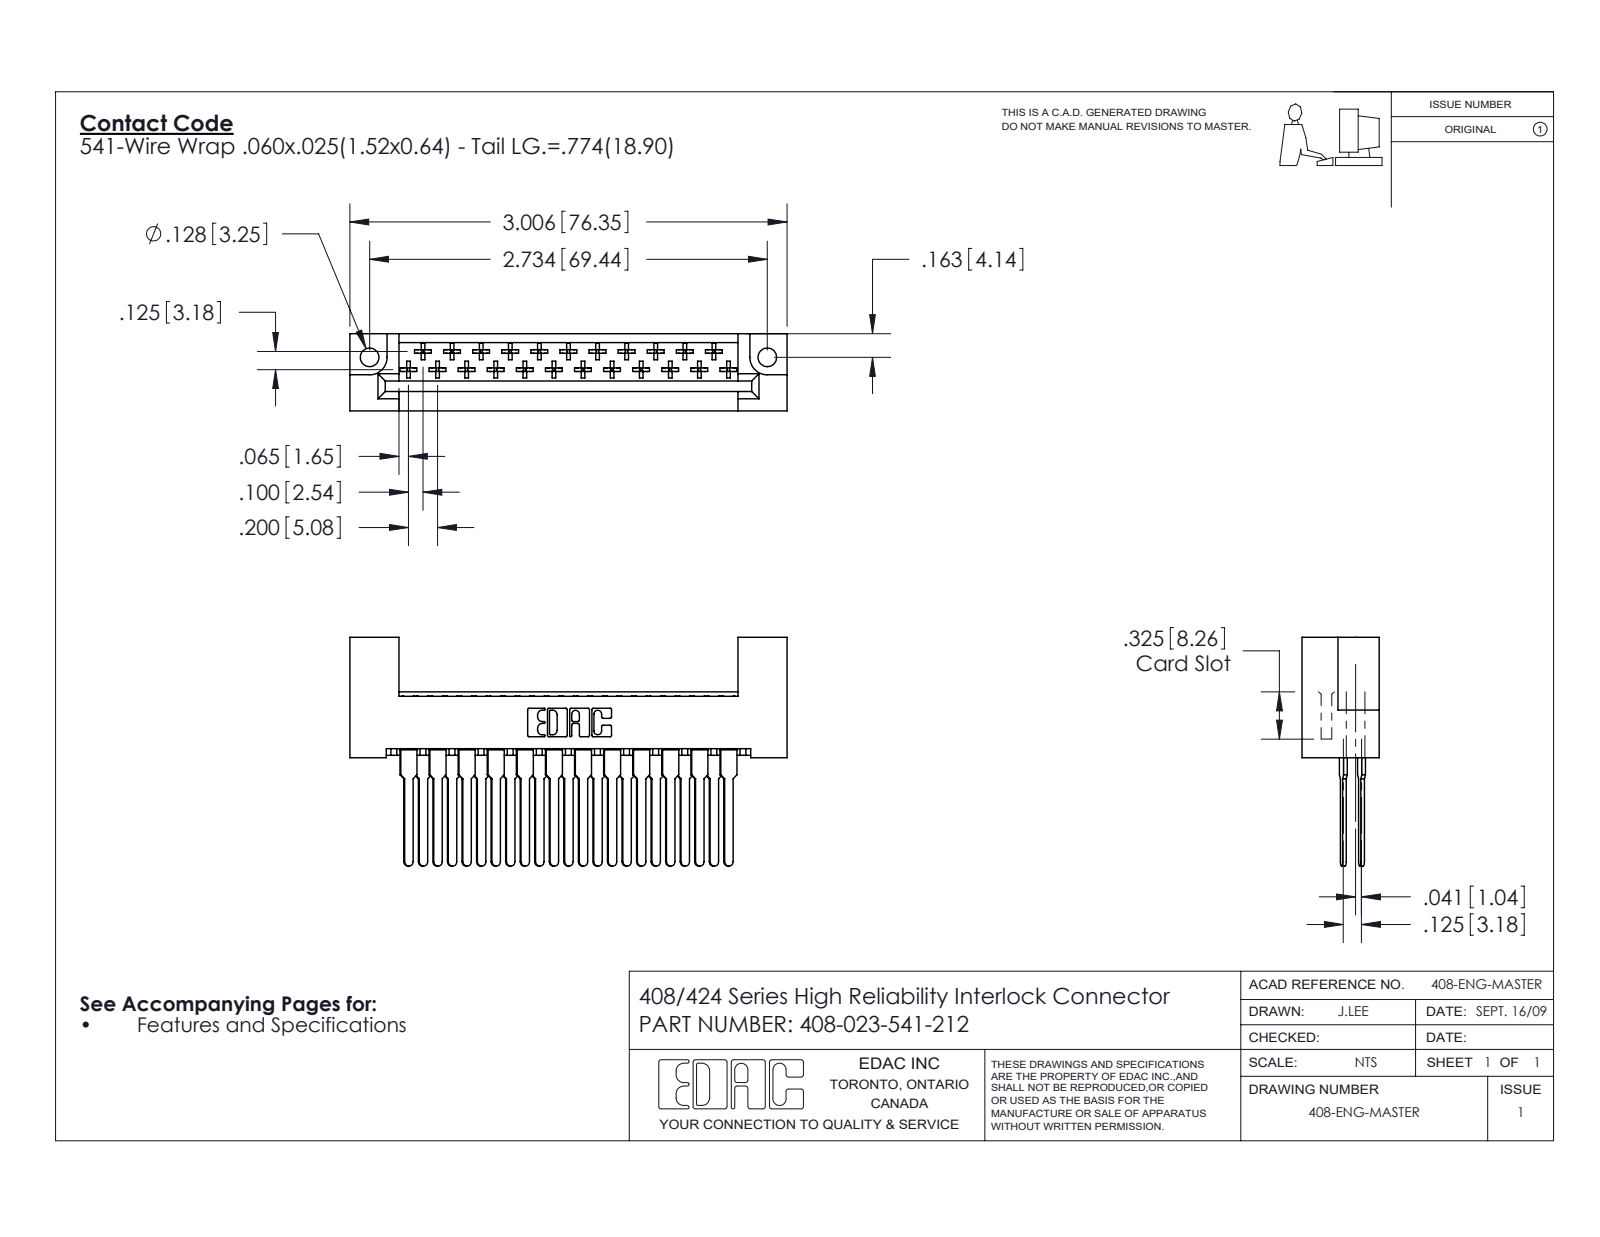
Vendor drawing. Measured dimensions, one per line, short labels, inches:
name: 408-023-541-212; 408 Part_023 - 2; 408-290-001_408-290-141
written by: SolidWorks 2016 (CONFIG_CONTROL_DESIGN)
unit: in
bodies: 24 solids, 1358 faces (1009 planar, 257 cylindrical, 92 other)
size: 3.006 × 1.572 × 0.531
volume: 0.632 in³; area: 19.66 in²
holes: 2× ⌀0.128
rounds: 138× R0.01, 25× R0.02, 23× R0.03, 22× R0.01, 6× R0.007, 6× R0.031, 3× R0.026, 2× R0.12
face distances: 0.531, 0.125, 0.1, 0.025, 0.025, 0.104, 0.361, 0.235, 0.259, 0.091
hole spacings: 2.734
